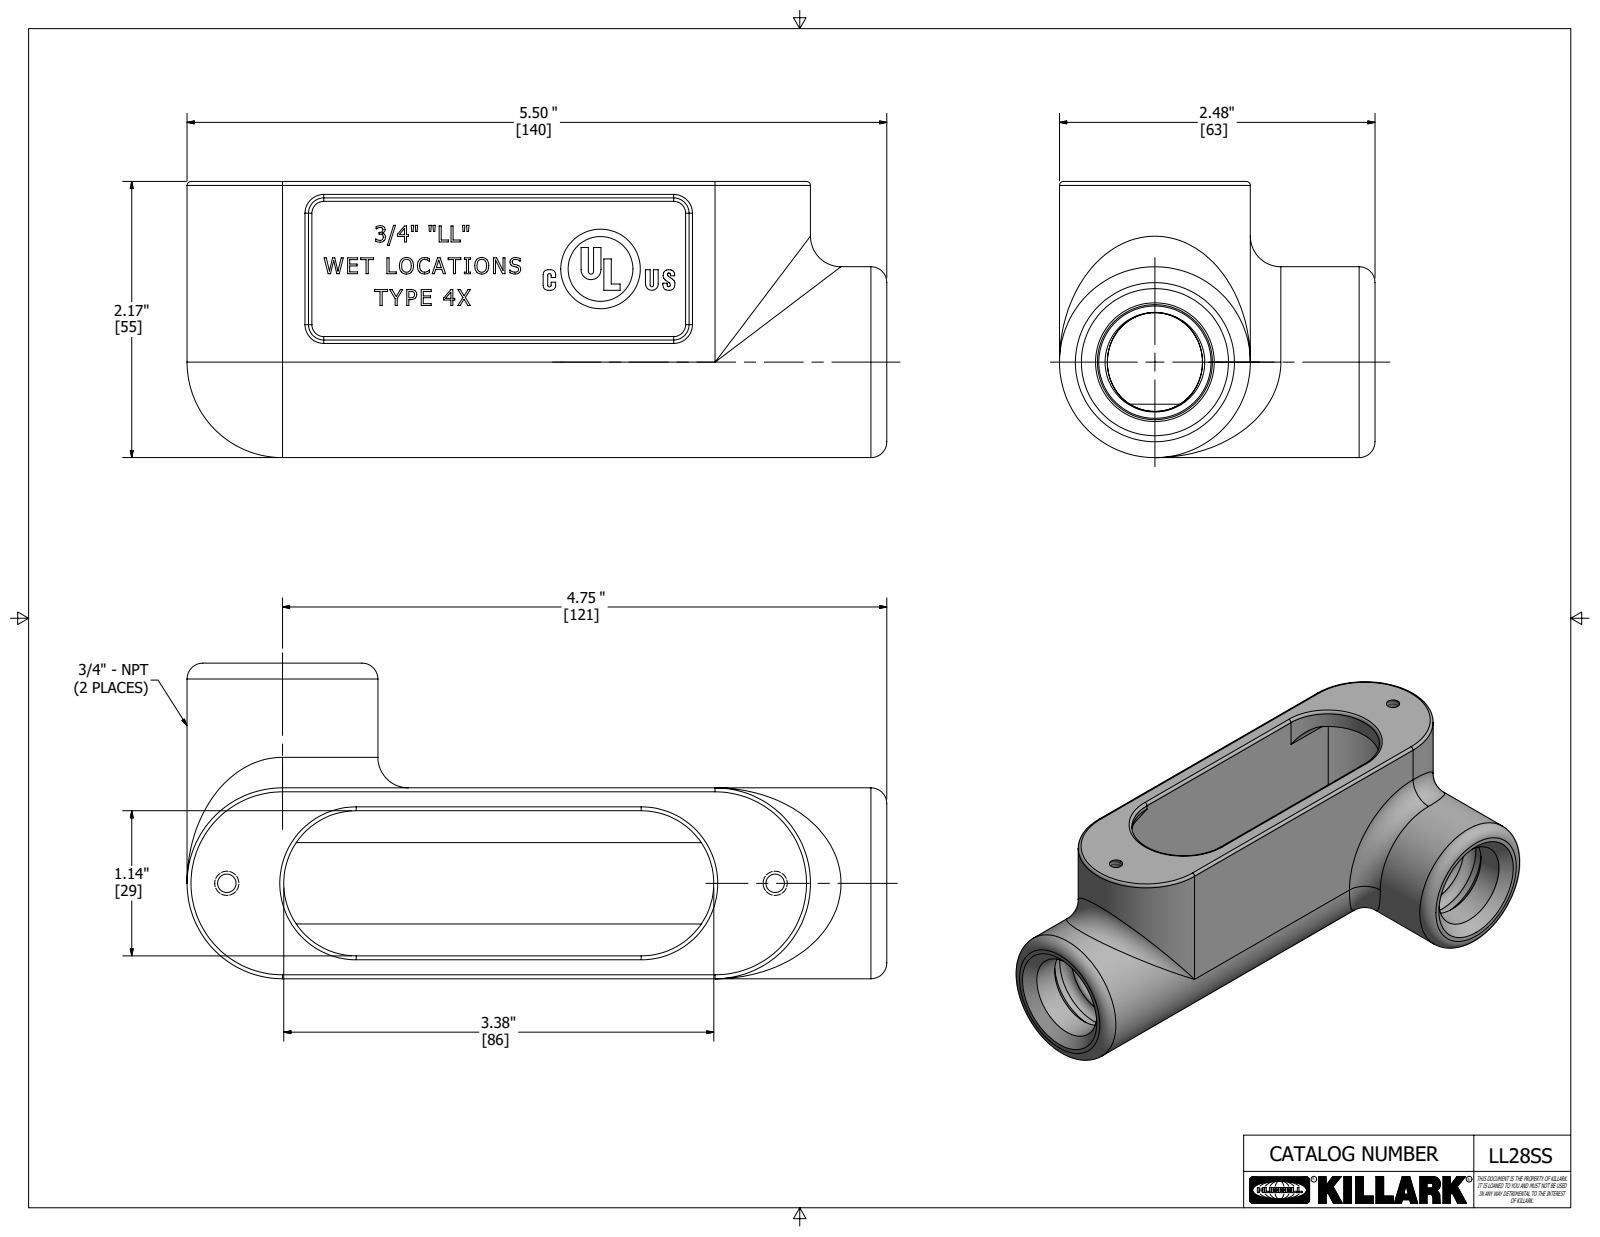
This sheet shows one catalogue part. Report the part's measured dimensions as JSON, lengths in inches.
{"part_name": "LL28SS", "step_written_by": "Autodesk Inventor 2020 (AUTOMOTIVE_DESIGN)", "units": "inches", "bodies": {"solids": 1, "faces": 499, "planar": 302, "cylindrical": 69, "other": 128}, "overall_size": [5.5, 2.48, 2.17], "volume_in3": 6.188, "surface_area_in2": 69.3, "round_holes": [[0.145, 2], [1.055, 2], [0.509, 1]], "round_bosses_or_shafts": [[1.5, 2], [0.625, 1]], "partial_cylinders_radius": [[0.031, 9], [0.031, 4], [0.038, 4], [0.57, 4], [0.013, 2], [0.013, 2], [0.125, 2], [0.25, 2]], "face_to_face_distances": [0.18, 1.32, 1.14, 0.149, 1.289, 1.469, 2, 0.031, 1.5, 1.8], "hole_center_spacings": [2.605, 4.31]}
